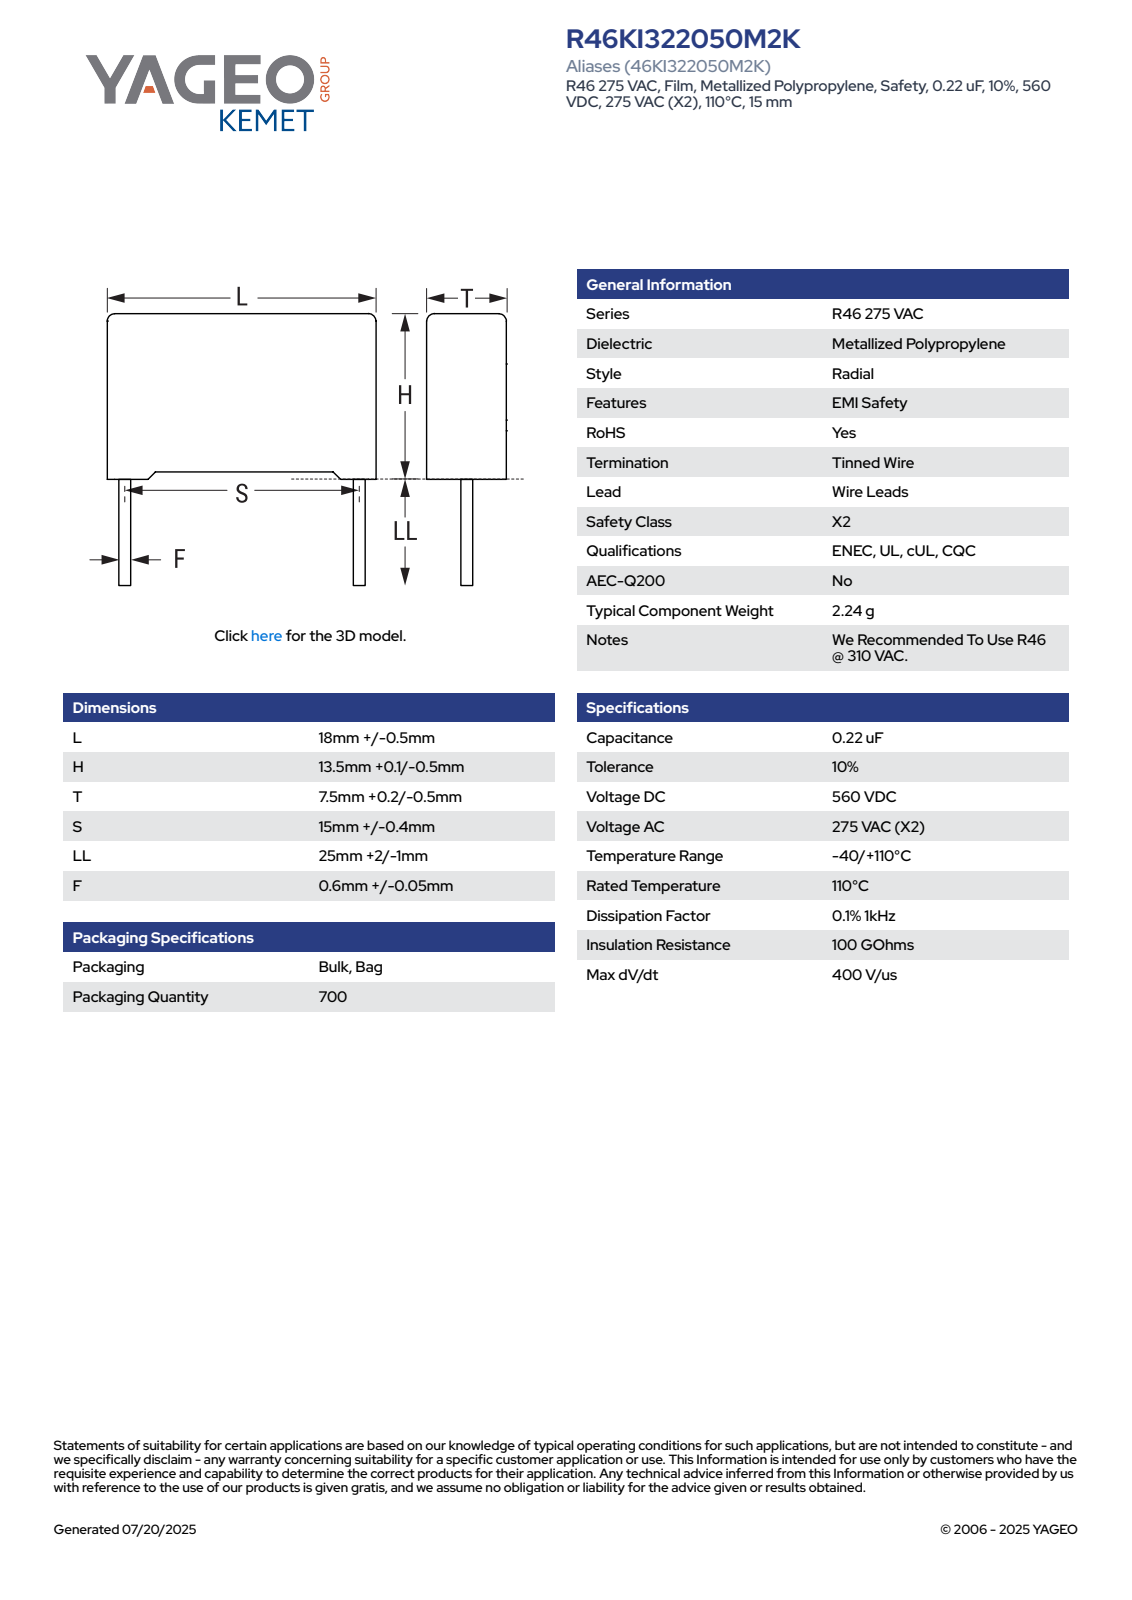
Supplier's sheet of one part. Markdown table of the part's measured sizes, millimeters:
| quantity | value |
| --- | --- |
| part name | CFR_RB2_18X13.5X7.5_L18.5H13.6T7.7S15LL27F0.65 |
| STEP written by | SolidWorks 2021 (AUTOMOTIVE_DESIGN) |
| units | millimeters |
| bodies | 4 solids, 85 faces (77 planar, 8 cylindrical, 0 other) |
| overall size | 40.6 × 18.5 × 7.71 |
| volume | 1 863 mm³ |
| surface area | 1 140 mm² |
| round bosses / shafts (diameter × count) | 0.65 × 2 |
| partial cylindrical surfaces (radius × count) | 0.5 × 4 |
| main face-to-face distances | 7.7, 12.85, 18.5, 0.62, 0.75, 13.6, 7.08, 0.47, 13.13, 17.88 |
